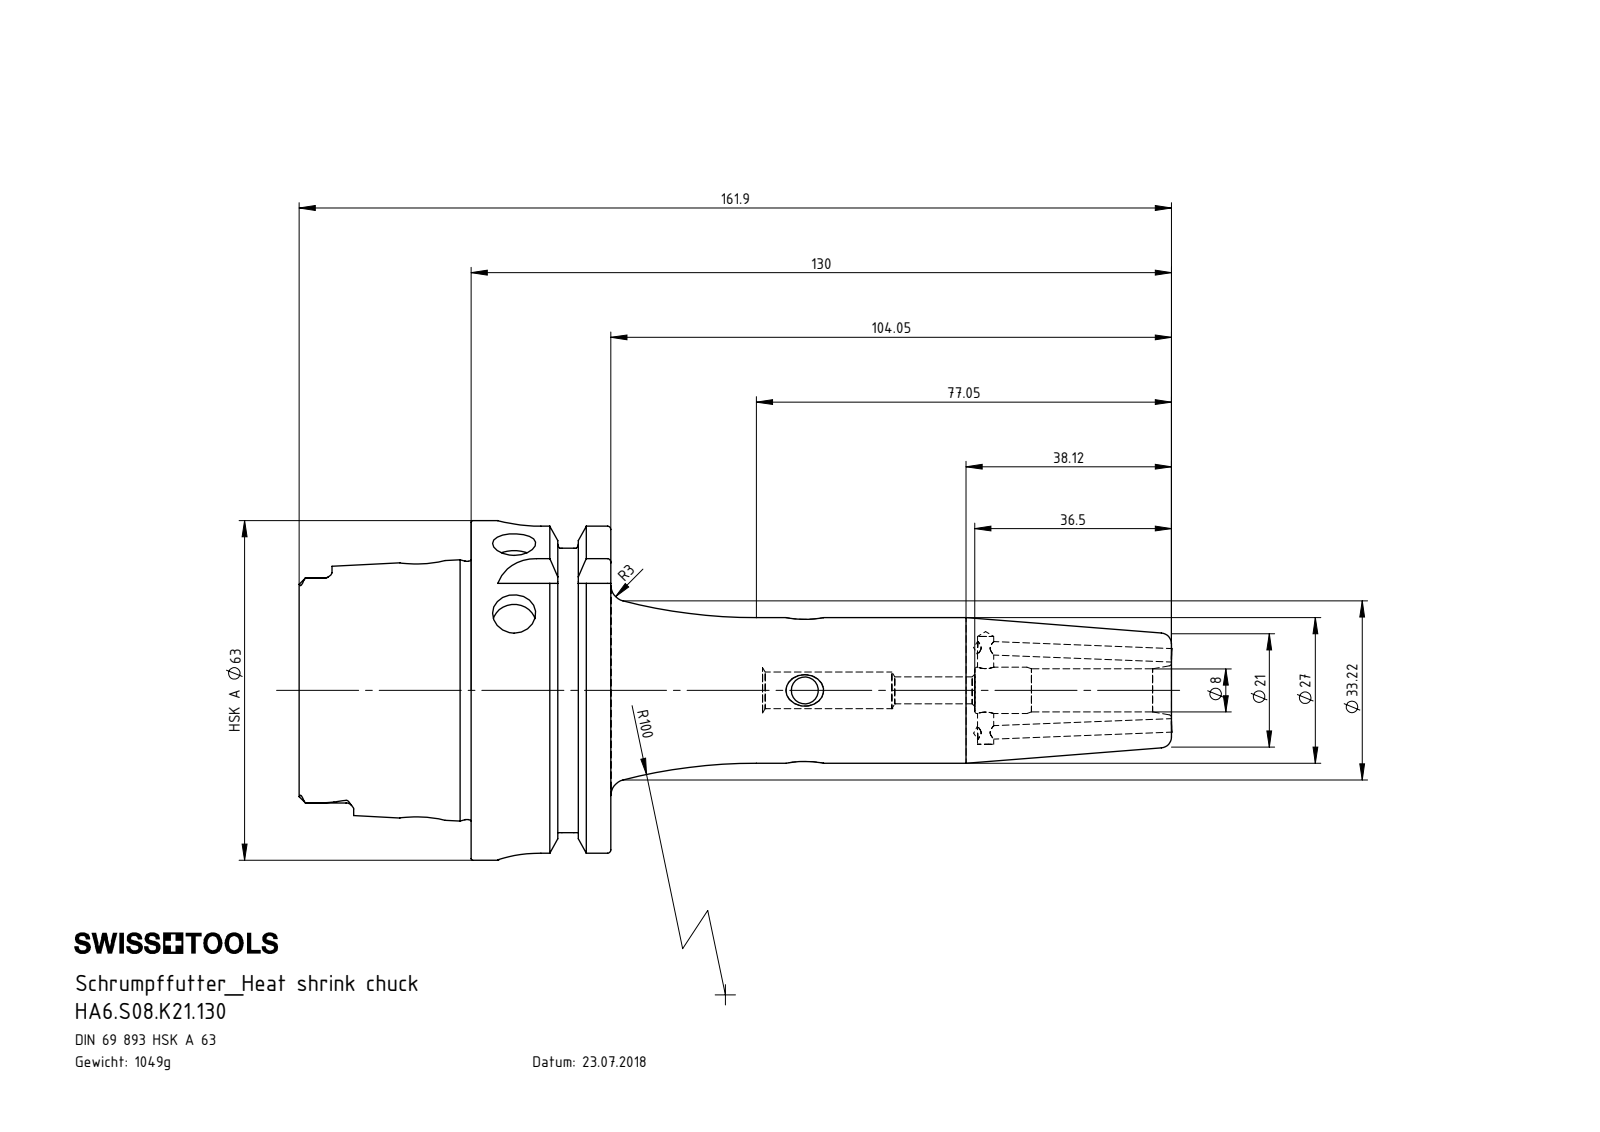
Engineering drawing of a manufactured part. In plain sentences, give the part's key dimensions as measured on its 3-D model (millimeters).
The part is named "ERU-CJ2.001.006; ERU-AN2.K01.016_A; HA6-S08.K21.130_C_Fertigbearbeitung; HA6.S08.K21.130". Its 3-D file was written by "SolidWorks 2012 (CONFIG_CONTROL_DESIGN)". It is 4 solids with 303 faces: 101 planar, 87 cylindrical and 115 other. Overall it measures 161.98 by 63 by 63 millimeters. Its volume is 133 660 cubic millimeters and its surface area 34 639 square millimeters. Round holes: 3 of diameter 5, 3 of diameter 8, 2 of diameter 2.5, 2 of diameter 3, 1 of diameter 6.8, 1 of diameter 7.5, 1 of diameter 8.4, 1 of diameter 8.6, 1 of diameter 10, 1 of diameter 17, 1 of diameter 19, 1 of diameter 34. Round bosses or shafts: 2 of diameter 3, 1 of diameter 63, 1 of diameter 54.95, 1 of diameter 47.93, 1 of diameter 27, 1 of diameter 6. Partial cylindrical surfaces (rounded edges, fillets, slot ends): 6 of radius 1.4, 4 of radius 2.88, 4 of radius 8. The main face-to-face distances are 25.95, 16, 9.95, 31.9, 41.85, 57.85, 52.8, 21.8, 11.85, 53.7. The hole center spacings are 33.55, 54.95, 70.95, 104.5.
